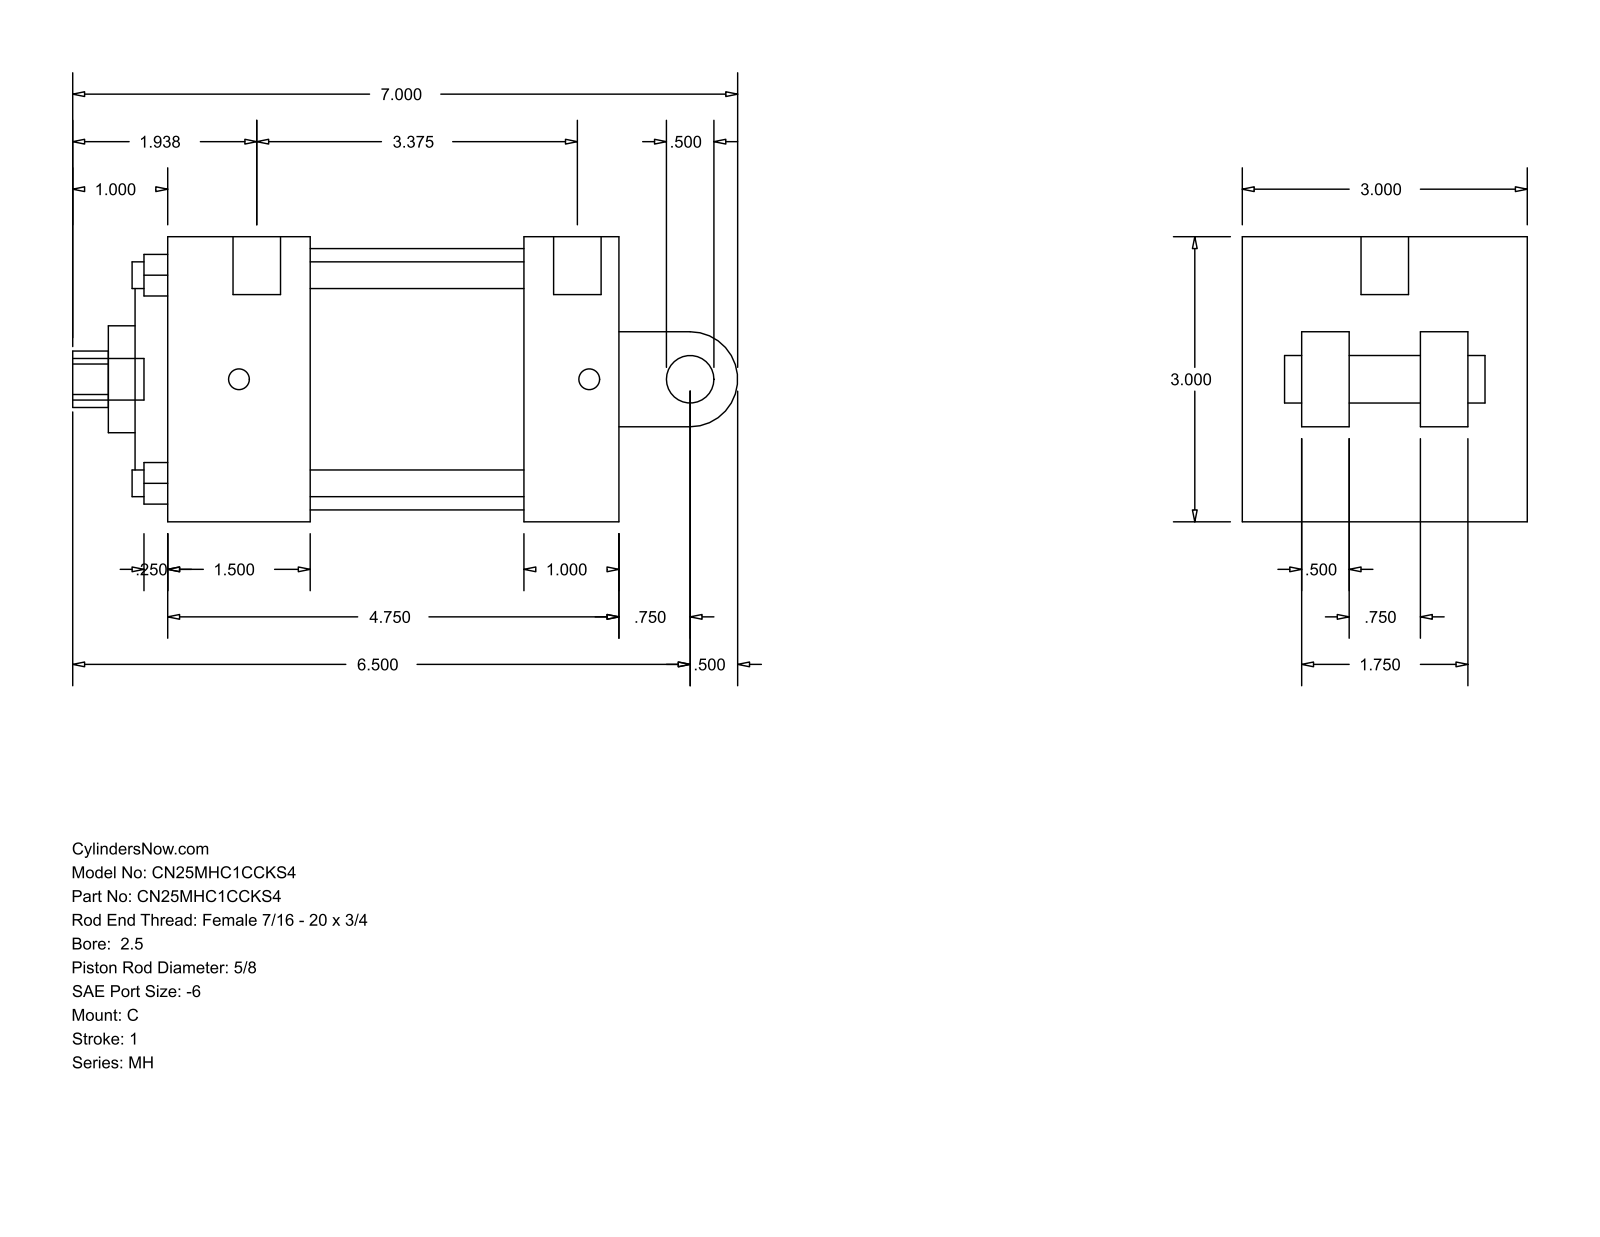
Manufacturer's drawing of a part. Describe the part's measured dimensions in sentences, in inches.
The part is named "MH_C__0250_0.625". Its 3-D file was written by "GSSL Pune (CONFIG_CONTROL_DESIGN)". It is 0 solids with 101 faces: 71 planar, 30 cylindrical and 0 other. Overall it measures 7 by 3 by 3 inches. Round holes: 4 of diameter 0.281, 2 of diameter 0.219, 1 of diameter 0.5, 1 of diameter 0.625, 1 of diameter 1.125, 1 of diameter 2.187, 1 of diameter 2.75. Round bosses or shafts: 2 of diameter 0.5, 2 of diameter 0.219, 1 of diameter 0.437. Partial cylindrical surfaces (rounded edges, fillets, slot ends): 1 of radius 0.297, 1 of radius 0.5. The main face-to-face distances are 3, 1, 4.75, 0.625, 2.25, 3.75, 1.5, 3.25, 0.344, 1.844. The hole center spacings are 1.548, 2.19, 3.097, 0.125.
